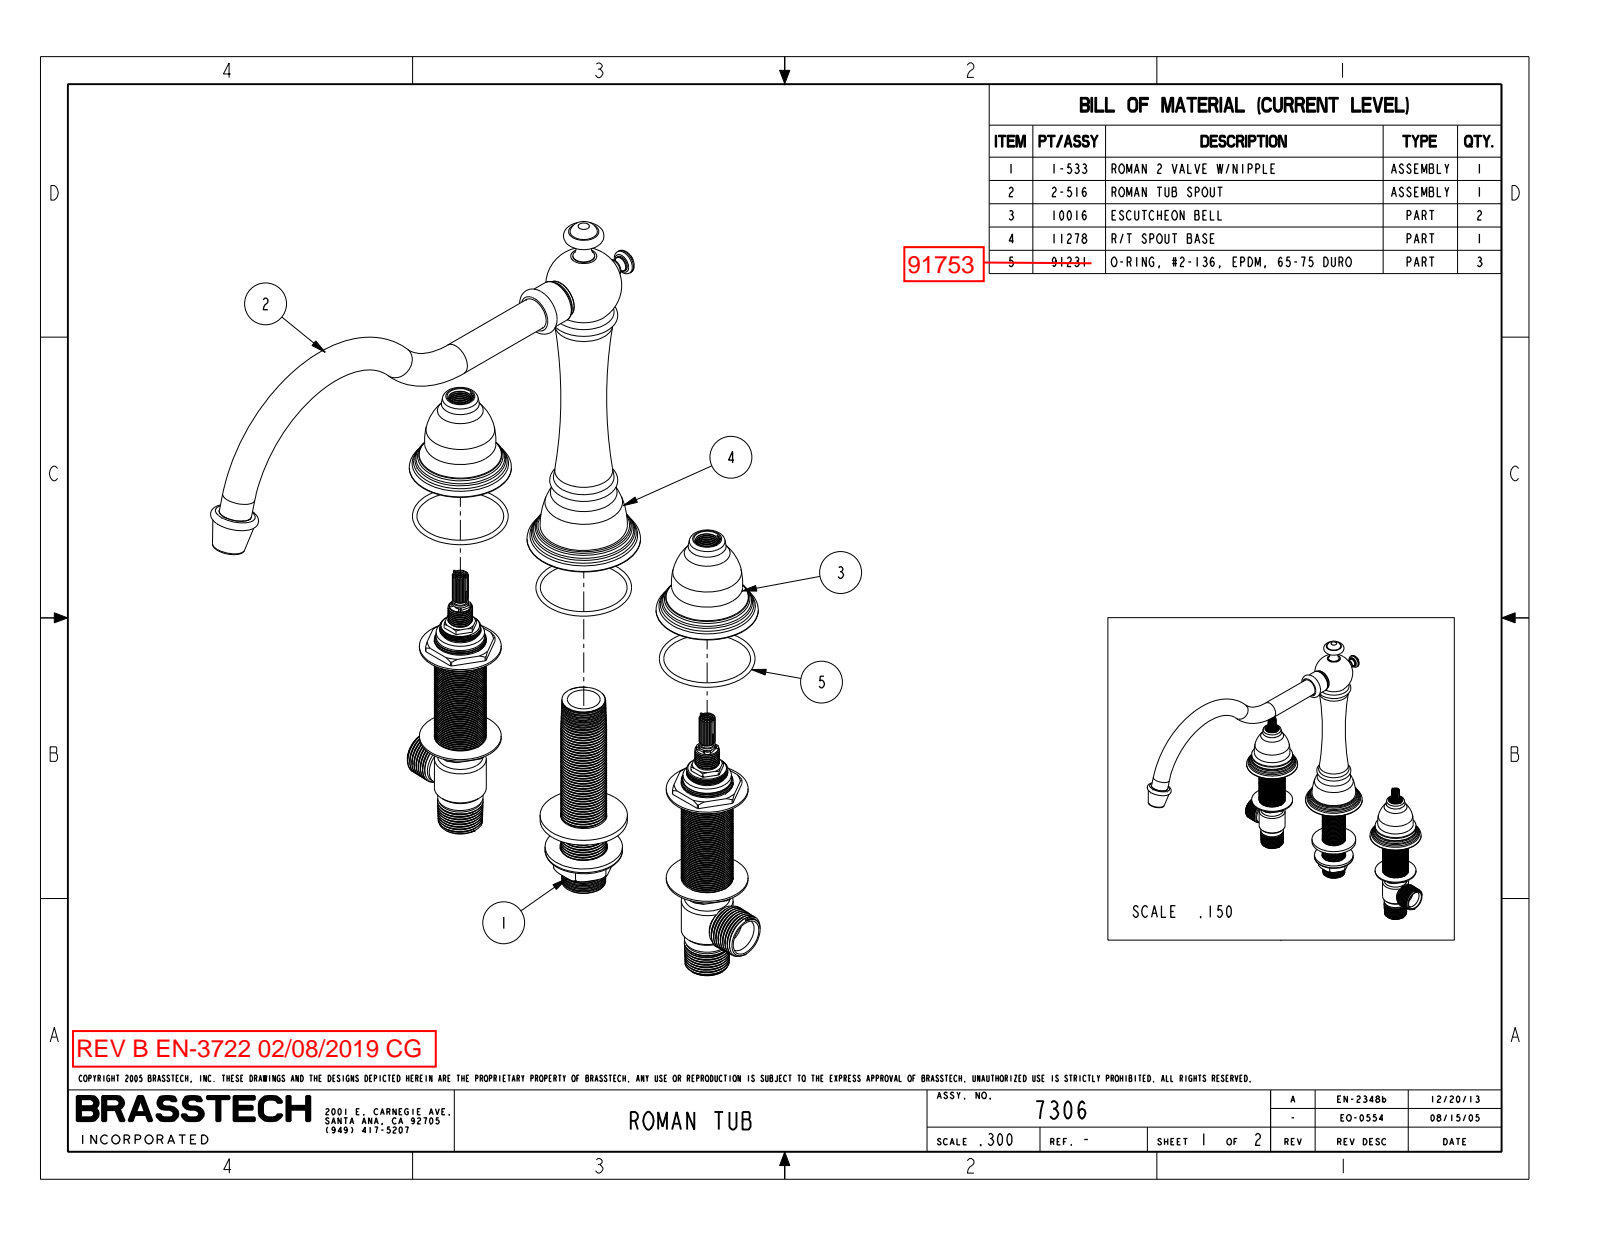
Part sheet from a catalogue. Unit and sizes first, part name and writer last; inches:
Units: inches
Overall size (bounding box): 13.349 × 10.34 × 9.37
Round holes (diameter × count): ⌀0.201 ×3, ⌀0.25 ×2, ⌀0.5 ×2, ⌀0.508 ×2, ⌀0.62 ×2, ⌀0.665 ×2, ⌀0.755 ×2, ⌀0.83 ×2, ⌀0.88 ×2, ⌀0.964 ×2, ⌀1 ×2, ⌀1.041 ×2
Round bosses / shafts (diameter × count): ⌀0.043 ×4, ⌀2.34 ×2, ⌀1.875 ×2, ⌀1.182 ×2, ⌀1.11 ×2, ⌀1.034 ×2, ⌀0.945 ×2, ⌀0.941 ×2
Partial cylindrical surfaces — rounded edges, fillets, slot ends (radius × count): R0.04 ×10, R0.08 ×8, R0.05 ×2, R0.164 ×2, R0.187 ×2, R0.26 ×2, R0.3 ×2, R0.82 ×2
Main face-to-face distances: 0.063, 0.108, 0.045, 1.353, 1.29, 1.245, 0.27, 0.207, 0.162, 1.083
Hole centre spacings: 4, 8
Volume: 17.5 in³ · Surface area: 346.1 in²
Bodies: 22 solids, 1674 faces (332 planar, 683 cylindrical, 659 other)
Part name (STEP PRODUCT): 11278_AF0; 11279; 10394; 10411 (+8 more)
STEP written by: PRO/ENGINEER BY PARAMETRIC TECHNOLOGY CORPORATION, 2009300 (CONFIG_CONTROL_DESIGN)
